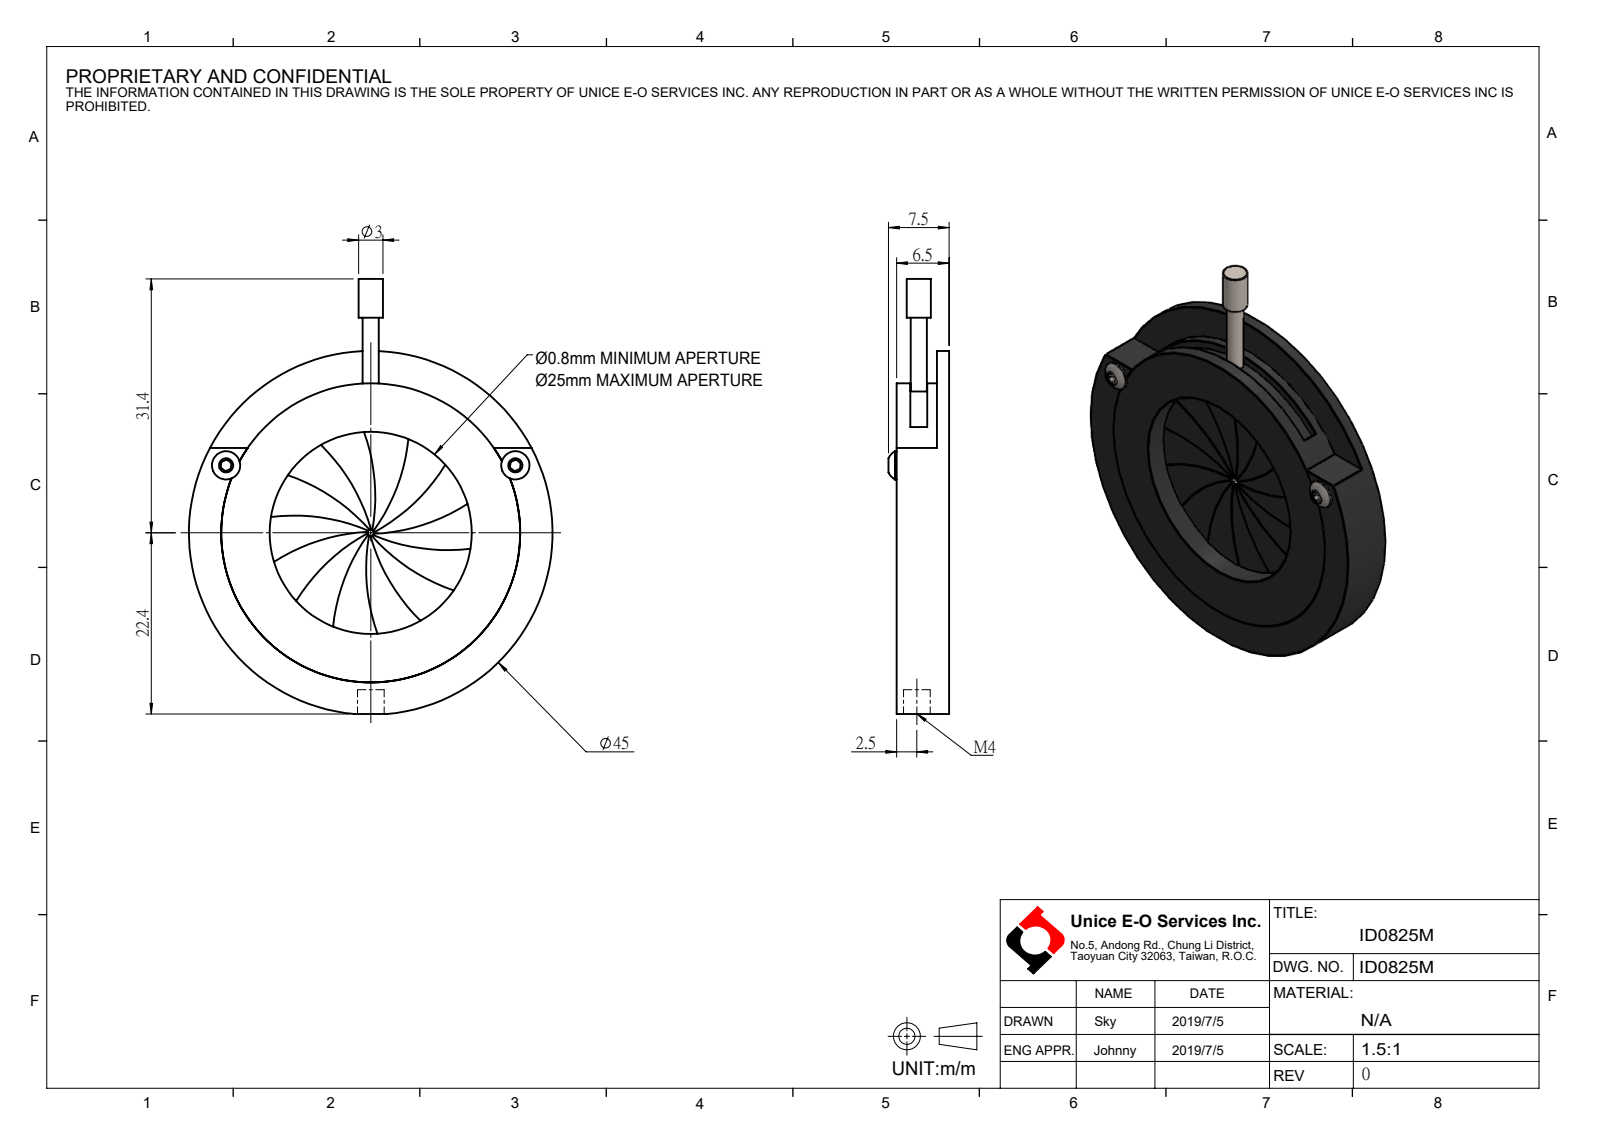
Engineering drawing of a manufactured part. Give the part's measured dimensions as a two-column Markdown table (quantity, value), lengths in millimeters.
| quantity | value |
| --- | --- |
| part name | ID0825M |
| STEP written by | SolidWorks 2016 (AUTOMOTIVE_DESIGN) |
| units | millimeters |
| bodies | 0 solids, 116 faces (56 planar, 56 cylindrical, 4 other) |
| overall size | 53.81 × 45 × 7.5 |
| round holes (diameter × count) | 0.8 × 1, 3.3 × 1, 25 × 1, 34 × 1, 37 × 1 |
| round bosses / shafts (diameter × count) | 3.5 × 2, 45 × 1, 3 × 1, 2 × 1 |
| partial cylindrical surfaces (radius × count) | 23.58 × 14, 17.5 × 1 |
| main face-to-face distances | 6.5, 1, 5.5, 2.7, 2.65, 2.85, 2.8, 3.8, 3.65, 3.85 |
